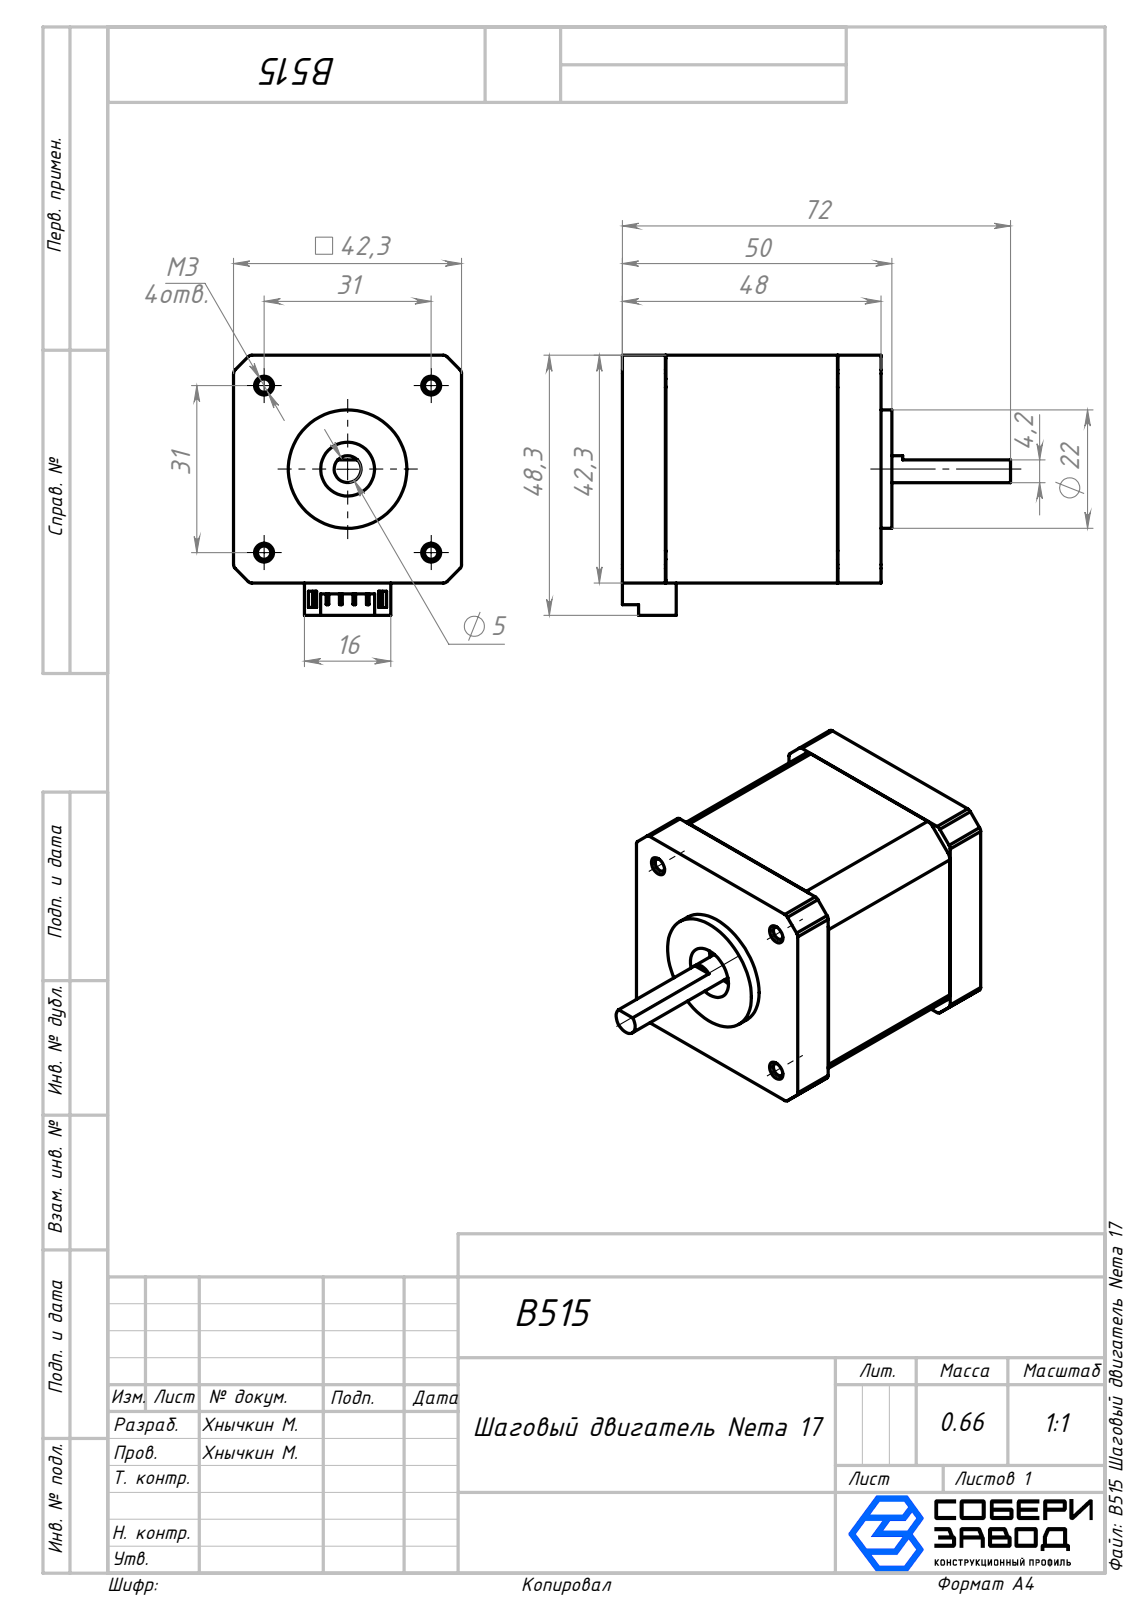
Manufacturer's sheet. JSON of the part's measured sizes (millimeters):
{"part_name": "B515 Шаговый двигатель Nema 17", "step_written_by": "SolidWorks 2026 (AUTOMOTIVE_DESIGN)", "units": "millimeters", "bodies": {"solids": 1, "faces": 150, "planar": 78, "cylindrical": 52, "other": 20}, "overall_size": [72, 48.3, 42.3], "volume_mm3": 84741, "surface_area_mm2": 15705, "round_holes": [[2.5, 4], [9, 1], [10, 1]], "round_bosses_or_shafts": [[0.5, 6], [22, 1], [5, 1]], "partial_cylinders_radius": [[1, 8], [2, 8]], "face_to_face_distances": [42.3, 40, 8, 8.1, 39.9, 31.9, 48, 32, 31.8, 2], "hole_center_spacings": [21.92, 31, 43.84]}
